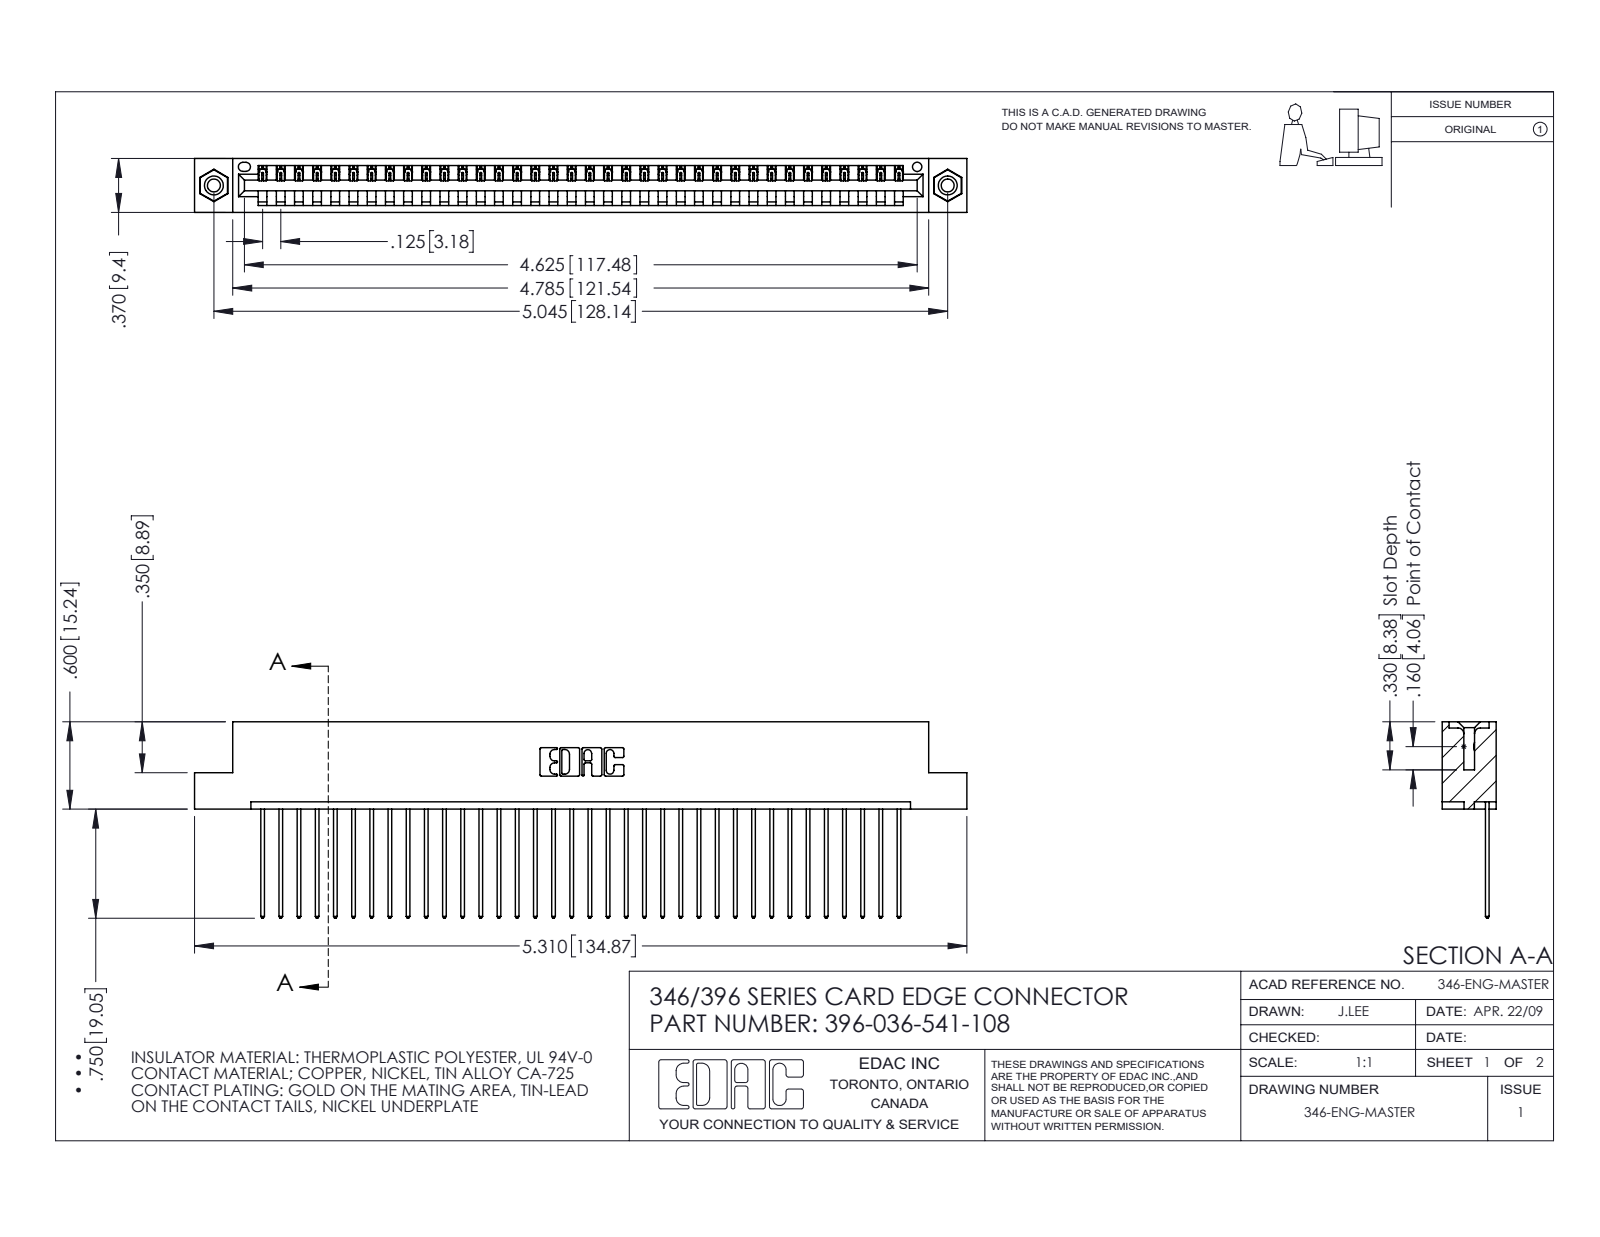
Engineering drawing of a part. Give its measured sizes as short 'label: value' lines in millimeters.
name: 345-250-001_345-250-003-102; 396-036-541-108; 345-292-001_345-293-141; 346 Part_Flush Mounting Lugs - 0.156 Dia-TI
written by: SolidWorks 2016 (CONFIG_CONTROL_DESIGN)
unit: mm
bodies: 39 solids, 2270 faces (1548 planar, 706 cylindrical, 16 other)
size: 134.9 × 34.3 × 9.4
volume: 13 000 mm³; area: 16 890 mm²
holes: 2× ⌀2.3, 2× ⌀3.2, 2× ⌀4, 1× ⌀1.6
bosses: 2× ⌀3.9
rounds: 72× R0.2, 72× R0.3, 22× R0.3, 6× R0.2, 6× R0.8, 3× R0.7, 2× R0.8, 2× R1
face distances: 1.2, 8.2, 9.4, 6.4, 1.8, 7.6, 0.6, 3.8, 5.6, 2.5
hole spacings: 6.2, 122.8, 128.1
